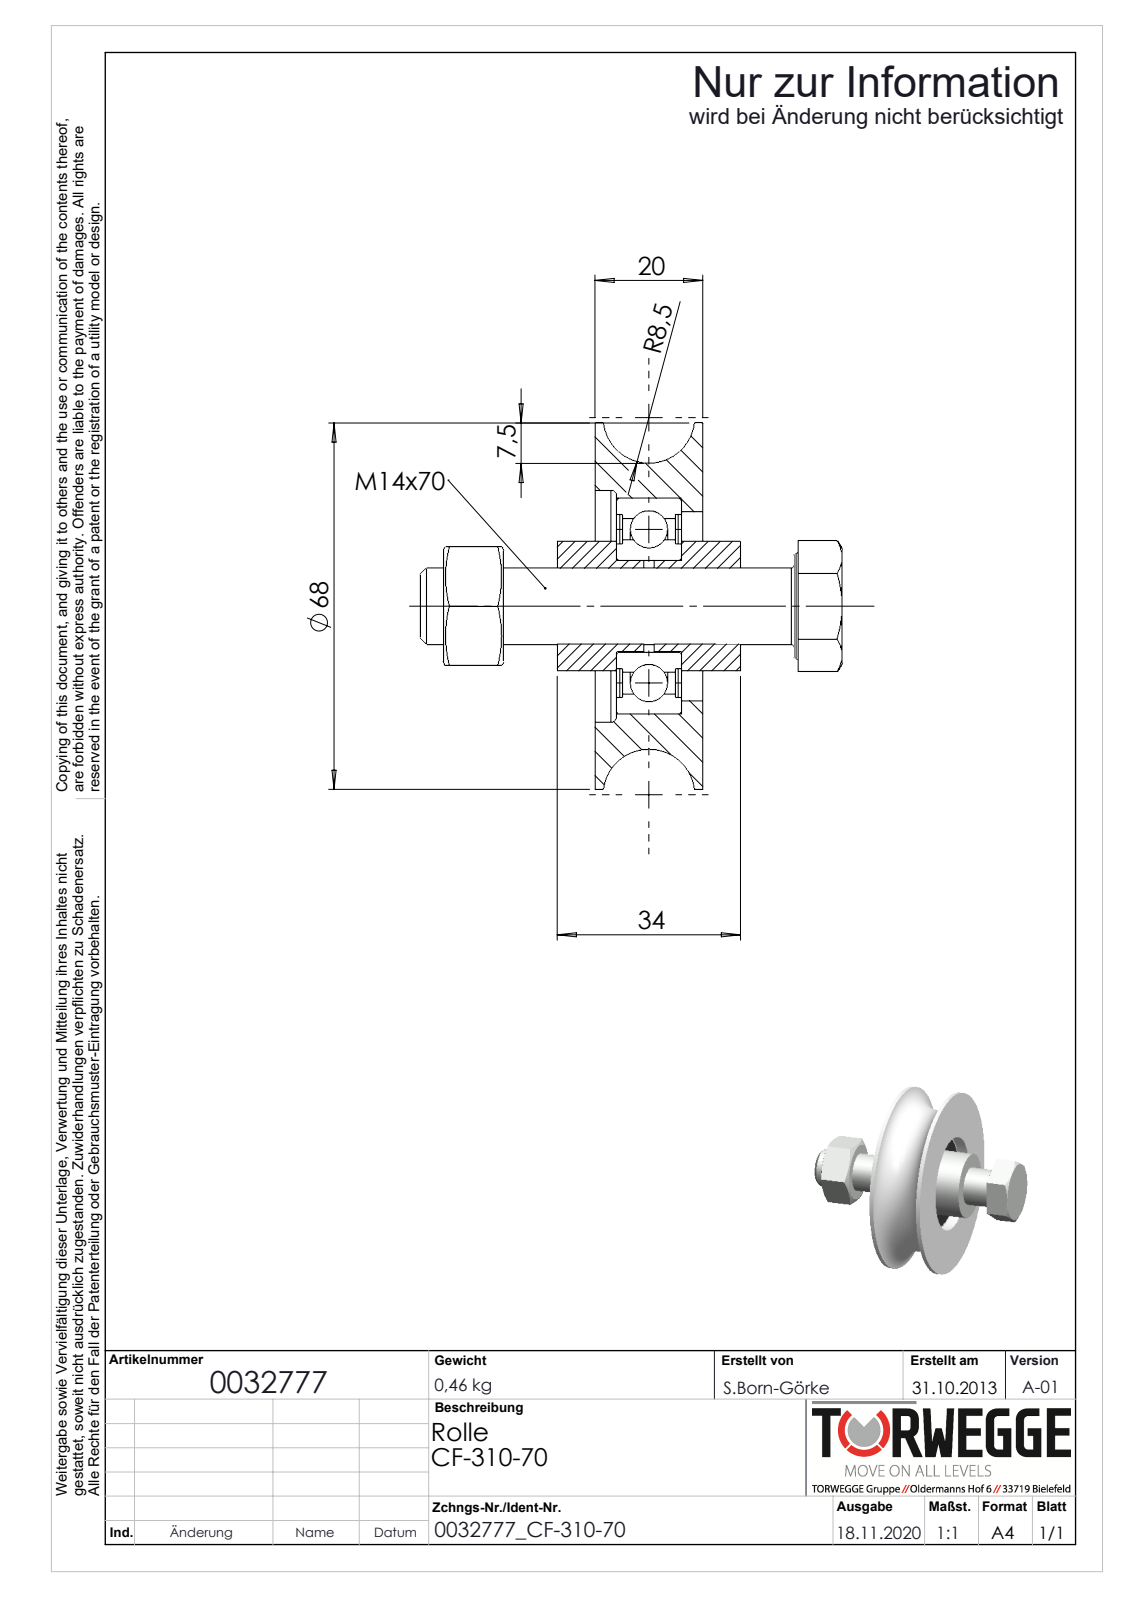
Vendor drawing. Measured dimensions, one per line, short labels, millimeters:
name: 0032777
written by: SolidWorks 2018 (AUTOMOTIVE_DESIGN)
unit: mm
bodies: 10 solids, 140 faces (40 planar, 54 cylindrical, 46 other)
size: 78.2 × 68 × 68
volume: 64 353 mm³; area: 33 674 mm²
holes: 1× ⌀11.84, 1× ⌀14, 1× ⌀17, 1× ⌀23.1, 1× ⌀32.5, 1× ⌀33.91, 1× ⌀35, 1× ⌀40, 1× ⌀43
bosses: 1× ⌀68, 1× ⌀24.5, 1× ⌀24, 1× ⌀16.9
face distances: 16, 4, 20, 0.56, 12, 4.56, 15.44, 11.44, 11, 7
